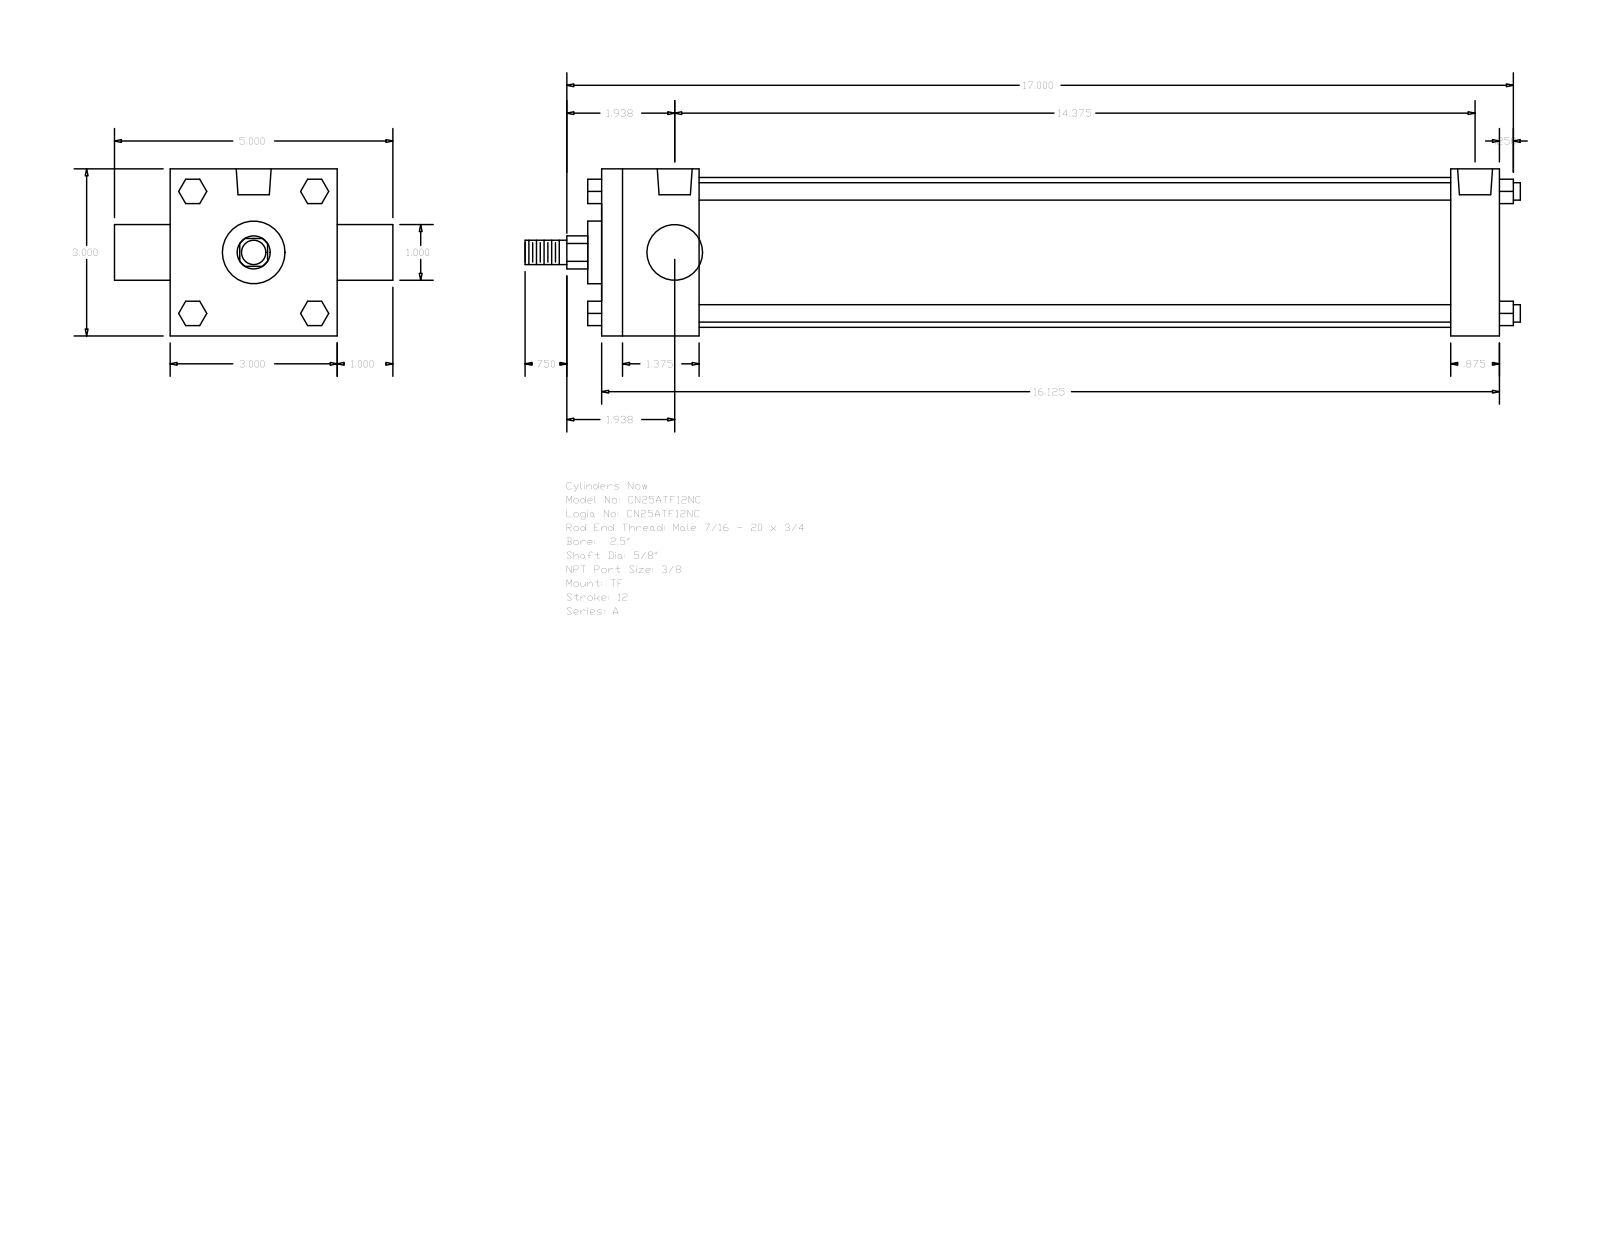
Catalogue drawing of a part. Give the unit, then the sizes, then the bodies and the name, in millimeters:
Units: millimetres
Overall size (bounding box): 454.02 × 127 × 76.2
Round holes (diameter × count): ⌀5.56 ×3, ⌀15.93 ×2
Round bosses / shafts (diameter × count): ⌀7.94 ×4, ⌀68.33 ×1, ⌀28.57 ×1, ⌀25.4 ×1, ⌀15.88 ×1, ⌀11.11 ×1
Partial cylindrical surfaces — rounded edges, fillets, slot ends (radius × count): R7.54 ×1
Main face-to-face distances: 76.2, 409.57, 44.45, 387.35, 342.9, 365.12, 22.22, 25.4, 101.6, 6.35
Hole centre spacings: 2.38, 367.51, 365.13, 369.89
Bodies: 0 solids, 120 faces (92 planar, 28 cylindrical, 0 other)
Part name (STEP PRODUCT): A_TF__0250_0.625
STEP written by: GSSL Pune (CONFIG_CONTROL_DESIGN)
